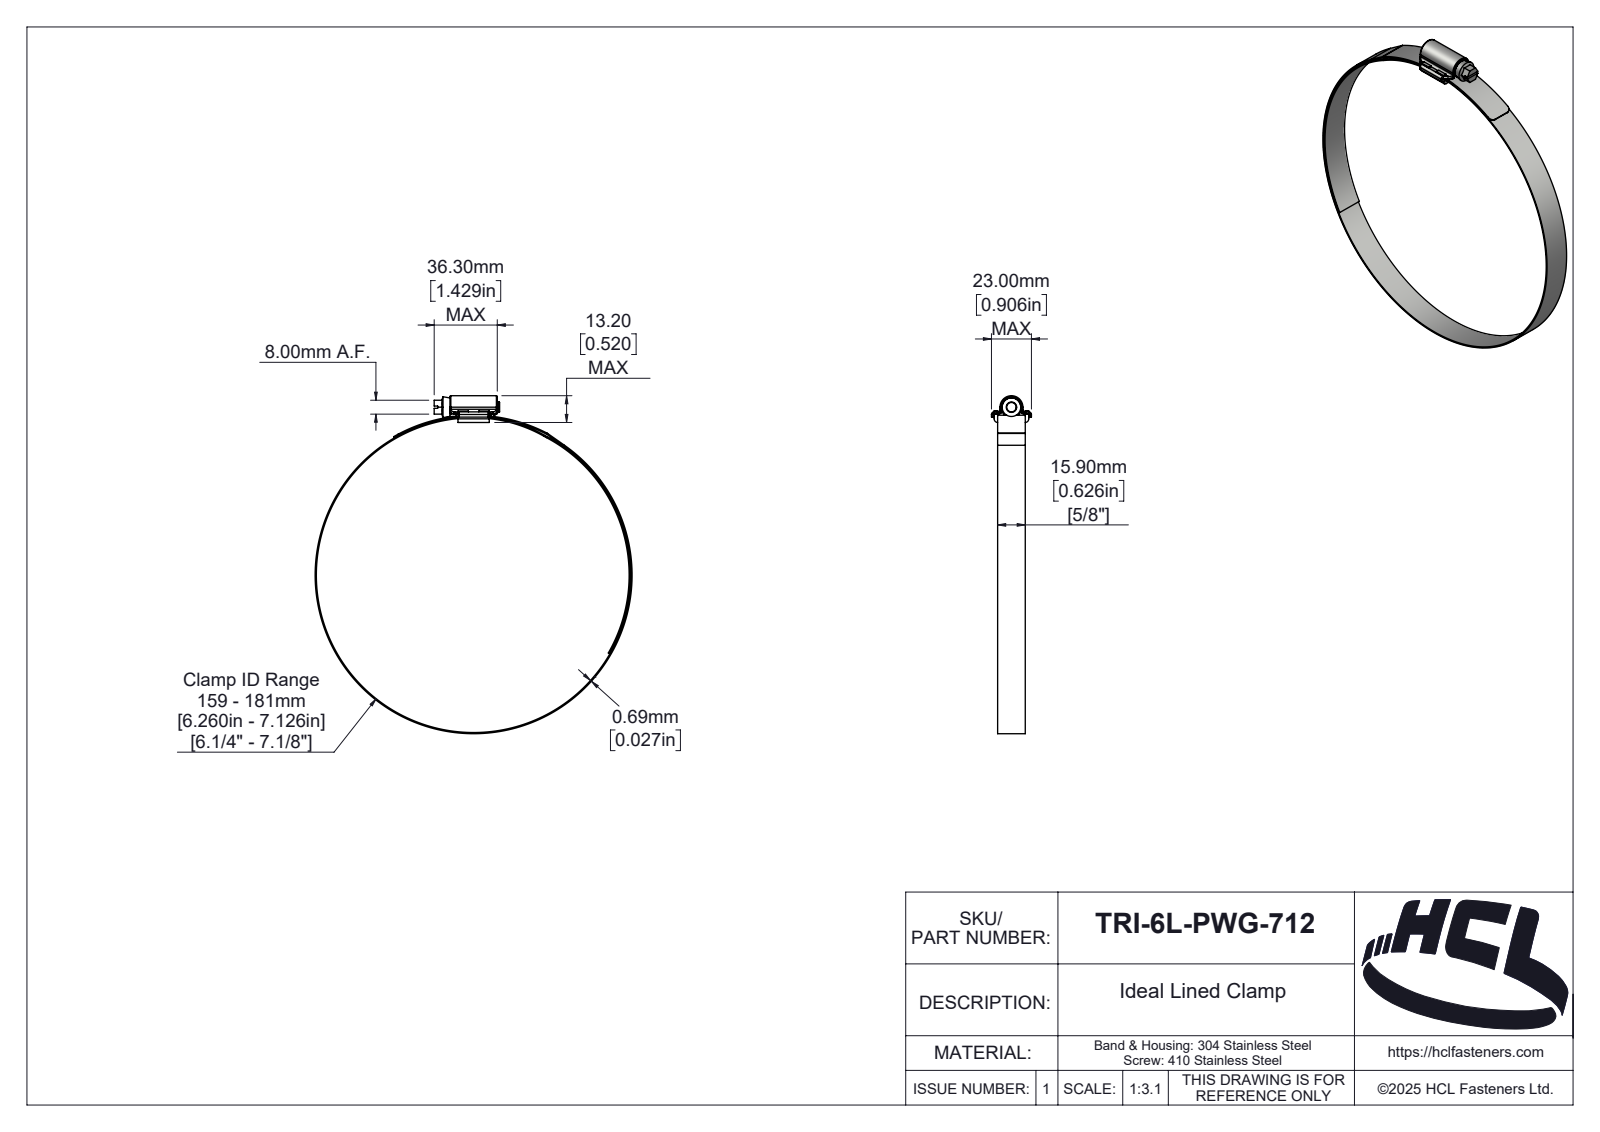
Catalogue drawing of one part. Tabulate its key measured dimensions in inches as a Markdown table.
| quantity | value |
| --- | --- |
| part name | TRI-6L-PWG-712 |
| STEP written by | SolidWorks 2025 (AUTOMOTIVE_DESIGN) |
| units | inches |
| bodies | 4 solids, 268 faces (87 planar, 102 cylindrical, 79 other) |
| overall size | 7.653 × 7.18 × 0.906 |
| volume | 0.858 in³ |
| surface area | 48.67 in² |
| round holes (diameter × count) | 7.126 × 1 |
| round bosses / shafts (diameter × count) | 7.18 × 1, 0.421 × 1, 0.236 × 1 |
| partial cylindrical surfaces (radius × count) | 0.039 × 14, 0.02 × 4, 0.059 × 4, 0.079 × 3, 0.004 × 2, 0.083 × 2, 0.118 × 2, 0.018 × 1 |
| main face-to-face distances | 0.626, 0.079, 0.027, 0.705, 0.193, 0.047, 0.179, 0.132, 0.604, 0.1 |
